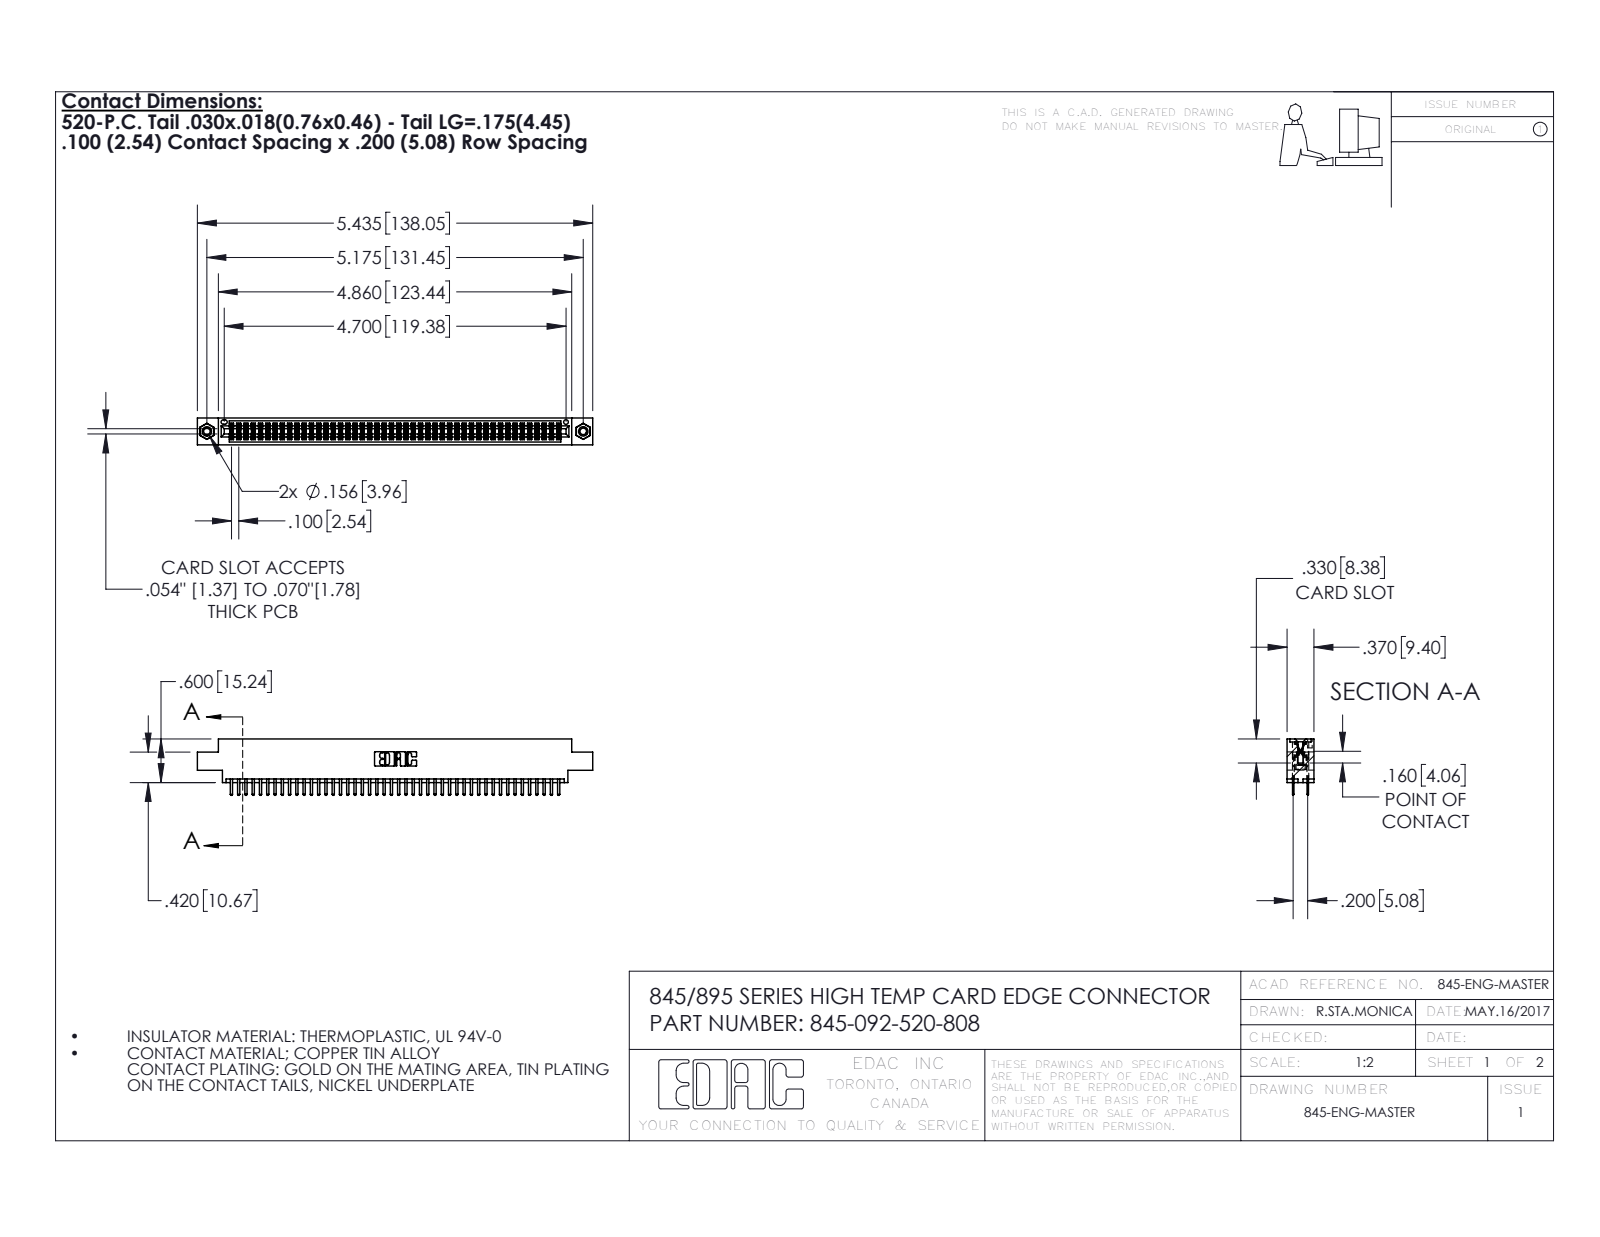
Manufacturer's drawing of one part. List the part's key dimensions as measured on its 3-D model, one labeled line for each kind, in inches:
Part name (STEP PRODUCT): 345 Part_0.170 Offset - 0.156 Dia-TI; 345-250-001_345-250-003-102; 345-292-001_345-293-120; 345-092-520-808
STEP written by: SolidWorks 2016 (CONFIG_CONTROL_DESIGN)
Units: inches
Bodies: 95 solids, 5158 faces (3336 planar, 1806 cylindrical, 16 other)
Overall size (bounding box): 5.435 × 0.775 × 0.37
Volume: 0.811 in³ · Surface area: 30.67 in²
Round holes (diameter × count): ⌀0.089 ×2, ⌀0.125 ×2, ⌀0.156 ×2, ⌀0.064 ×1
Round bosses / shafts (diameter × count): ⌀0.155 ×2
Partial cylindrical surfaces — rounded edges, fillets, slot ends (radius × count): R0.006 ×138, R0.01 ×96, R0.01 ×22, R0.007 ×6, R0.031 ×6, R0.026 ×3, R0.014 ×2, R0.019 ×2
Main face-to-face distances: 0.072, 0.298, 0.2, 0.37, 0.098, 0.272, 0.025, 0.225, 0.022, 0.072
Hole centre spacings: 0.27, 4.939, 5.175
